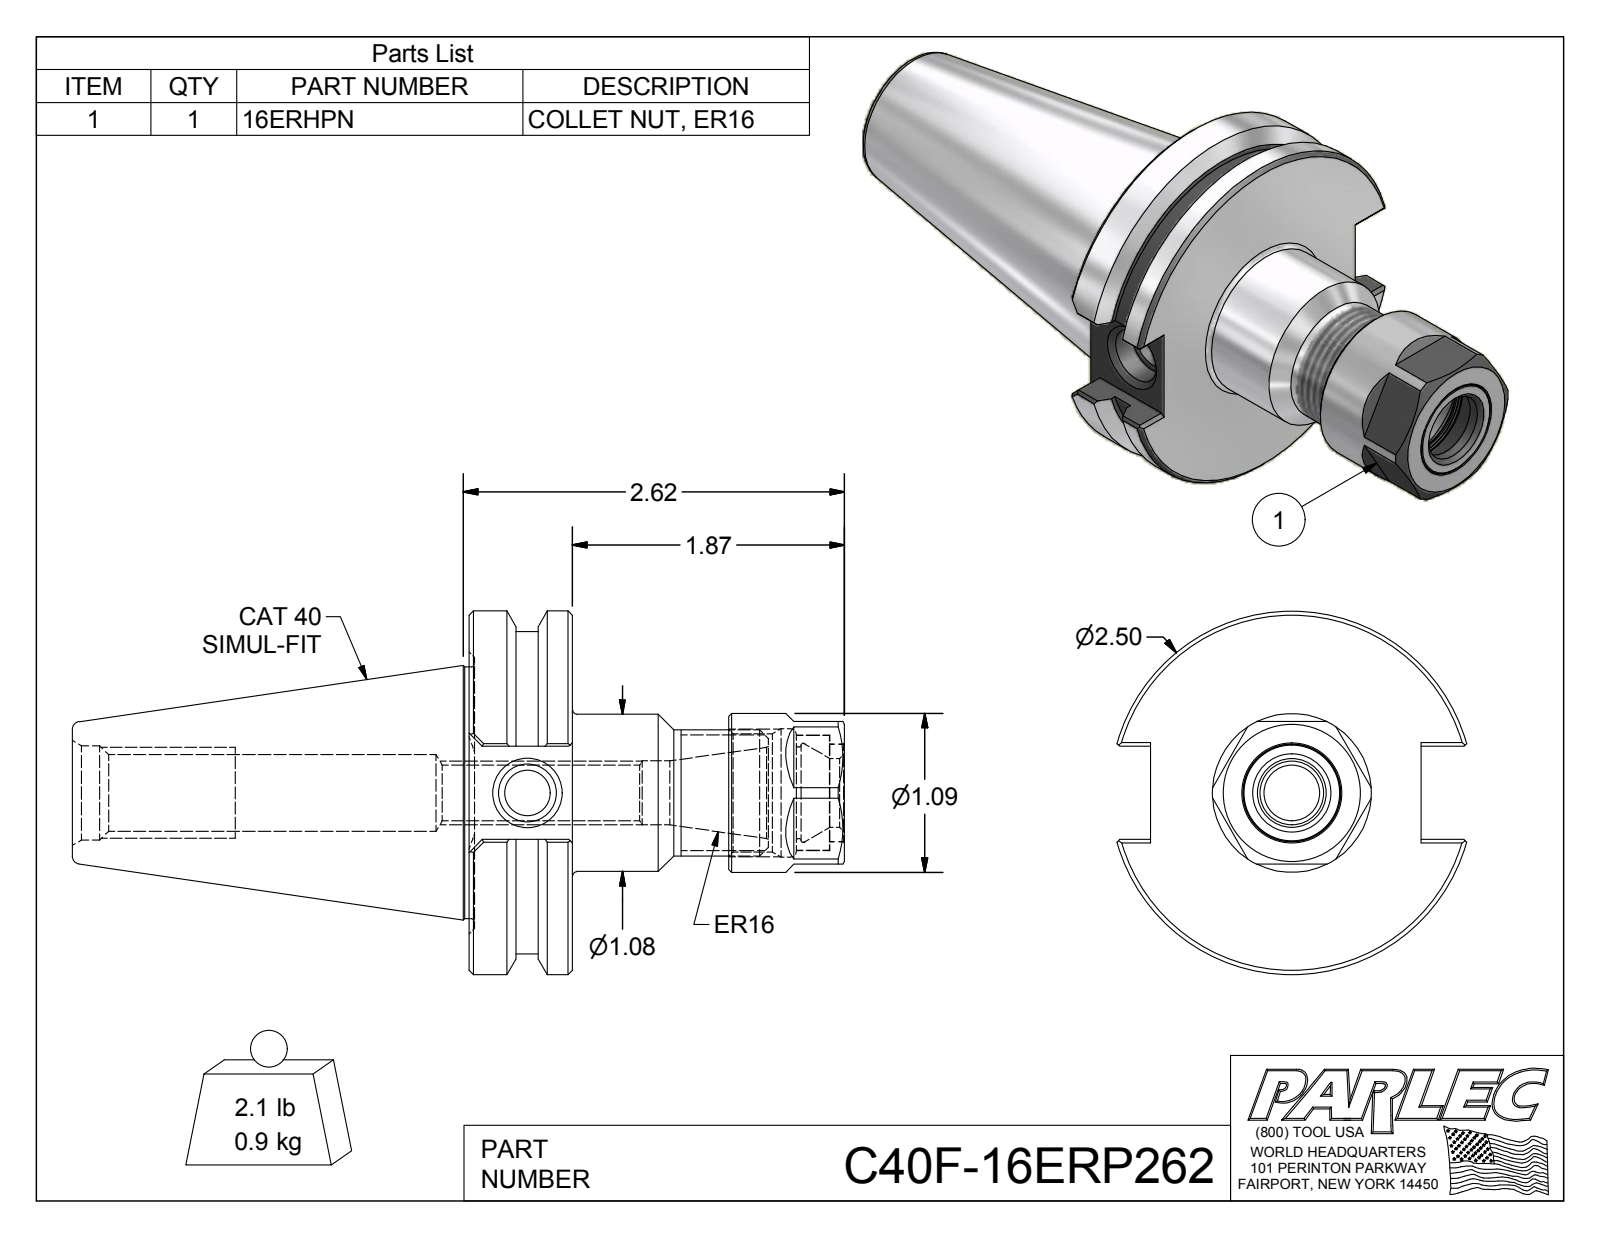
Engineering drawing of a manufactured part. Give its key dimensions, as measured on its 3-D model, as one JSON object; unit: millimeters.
{"part_name": "C40F-16ERP262; C40F-16ER2-1; 16ERHPN", "step_written_by": "Autodesk Inventor 2012 (AUTOMOTIVE_DESIGN)", "units": "millimeters", "bodies": {"solids": 3, "faces": 118, "planar": 52, "cylindrical": 25, "other": 41}, "overall_size": [134.8, 63.5, 61.1], "volume_mm3": 123000, "surface_area_mm2": 28900, "round_holes": [[8, 1], [9.7, 1], [10.1, 1], [11.2, 1], [12, 1], [13.4, 1], [16, 1], [16.5, 1], [17.1, 1], [17.3, 1], [20.2, 1], [20.7, 1]], "round_bosses_or_shafts": [[63.5, 1], [56.3, 1], [43.9, 1], [27.7, 1], [27.4, 1], [22, 1], [20.1, 1], [17, 1]], "face_to_face_distances": [18.1, 24.9, 65.6, 47.5, 47.2, 45.3, 27.3, 20.2, 16.3, 0.9]}
